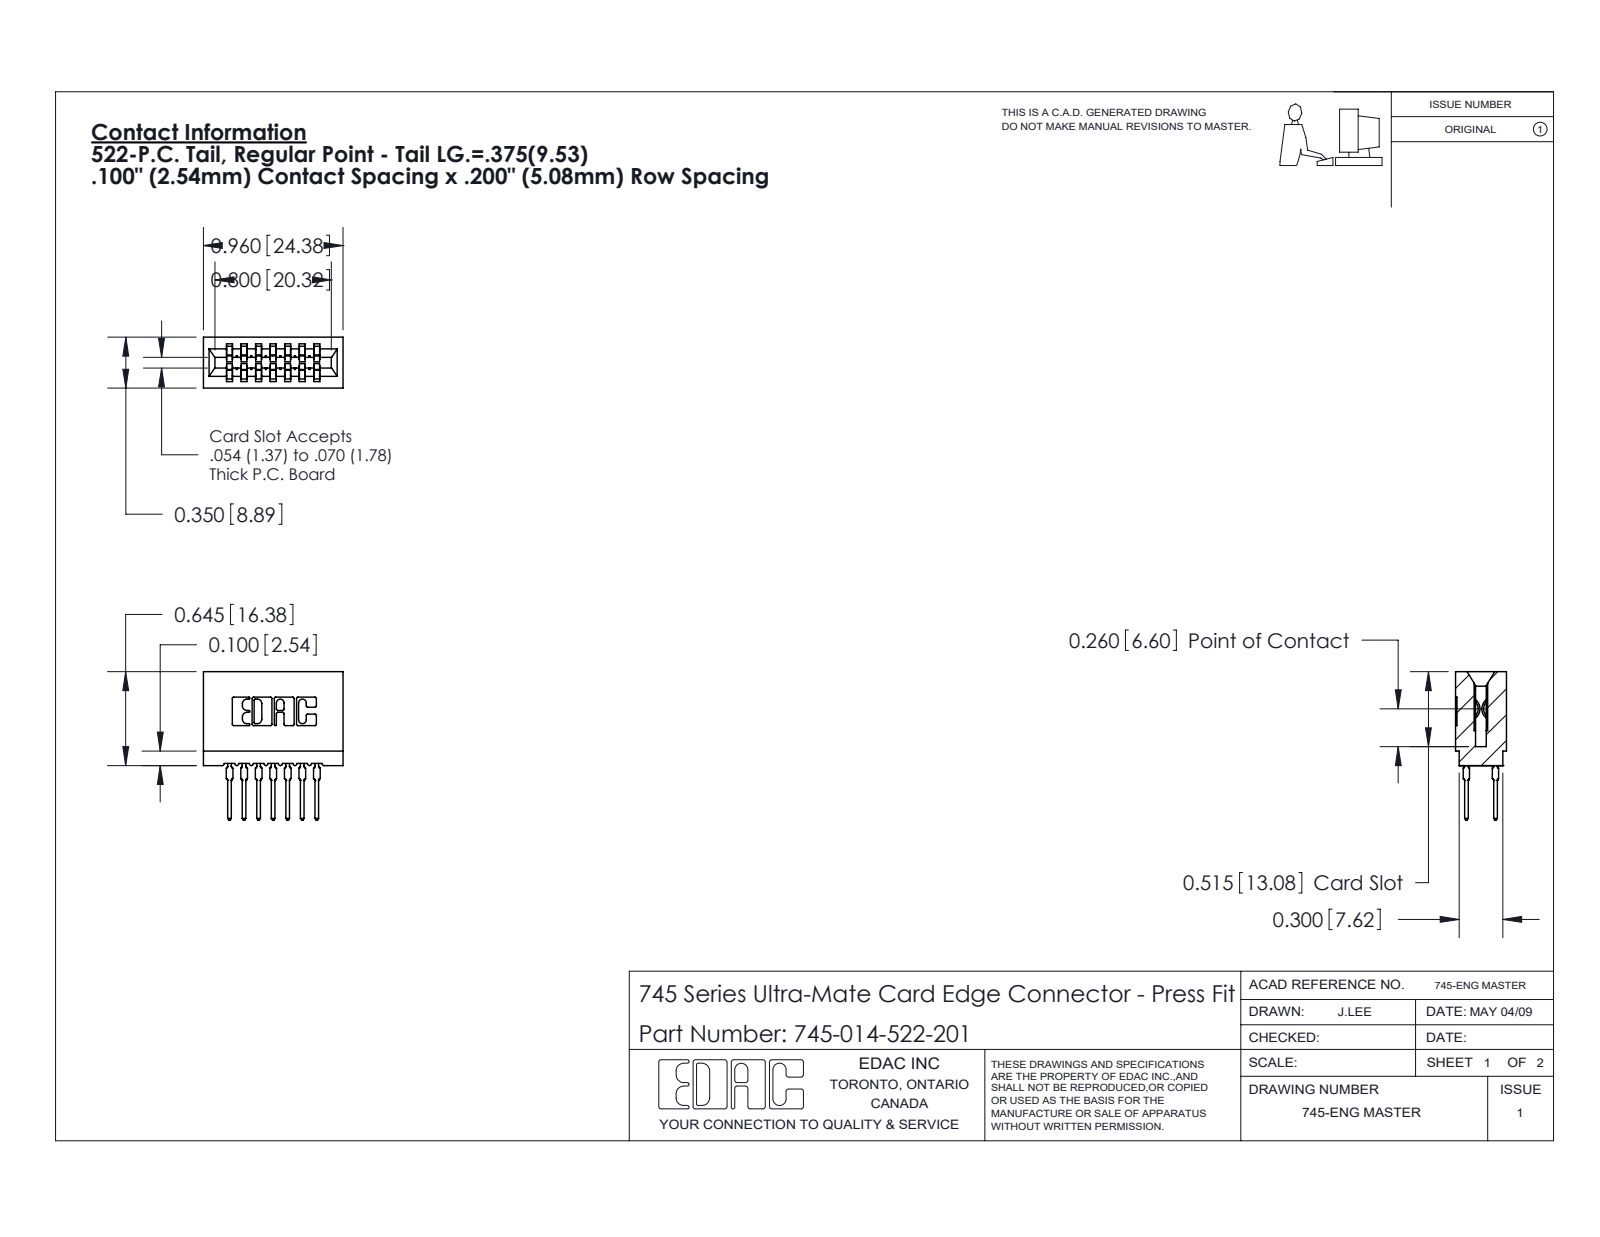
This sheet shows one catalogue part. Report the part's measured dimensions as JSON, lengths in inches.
{"part_name": "745-014-522-201; 745-292-001_522; 745 Part_Insulator Option - 01", "step_written_by": "SolidWorks 2020 (CONFIG_CONTROL_DESIGN)", "units": "inches", "bodies": {"solids": 15, "faces": 1348, "planar": 699, "cylindrical": 285, "other": 364}, "overall_size": [1.021, 0.96, 0.35], "volume_in3": 0.148, "surface_area_in2": 6.452, "partial_cylinders_radius": [[0.021, 28], [0.01, 22], [0.015, 14], [0.005, 8], [0.011, 8], [0.007, 6], [0.031, 6], [0.026, 3]], "face_to_face_distances": [0.1, 0.2, 0.3, 0.042, 0.142, 0.4, 0.058, 0.242, 0.158, 0.35]}
